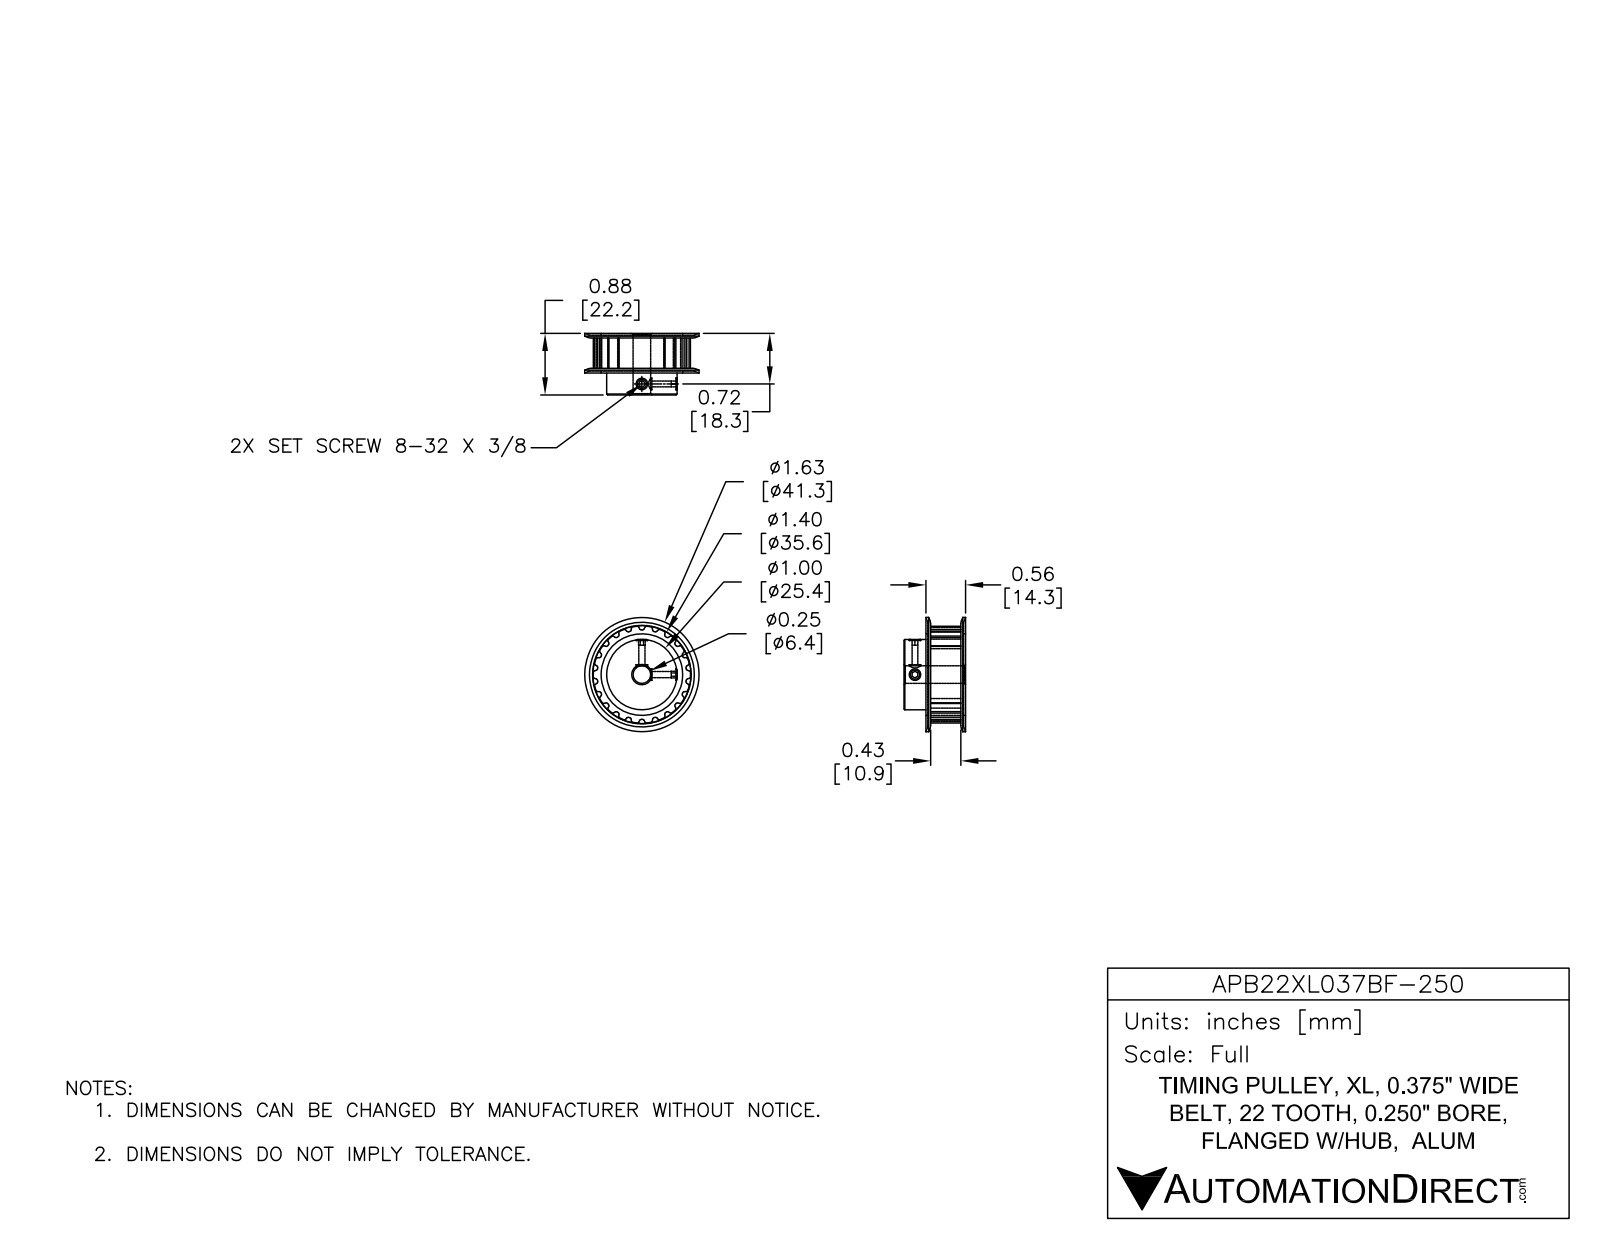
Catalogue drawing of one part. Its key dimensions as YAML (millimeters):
part_name: "APB22XL037BF-250"
step_written_by: "SolidWorks 2014 (AUTOMOTIVE_DESIGN)"
units: millimeters
bodies: {solids: 1, faces: 225, planar: 72, cylindrical: 131, other: 22}
overall_size: [41.27, 41.27, 22.23]
volume: 16226
surface_area: 6548
round_holes:
  - {diameter: 2.23, count: 2}
  - {diameter: 6.35, count: 1}
round_bosses_or_shafts:
  - {diameter: 25.4, count: 1}
partial_cylinders:
  - {radius: 0.38, count: 88}
  - {radius: 16.14, count: 1}
face_to_face_distances: [12.57, 0.83, 13.4, 22.23, 21.4, 8.83, 35.08, 12.48, 11.74, 9.66]
